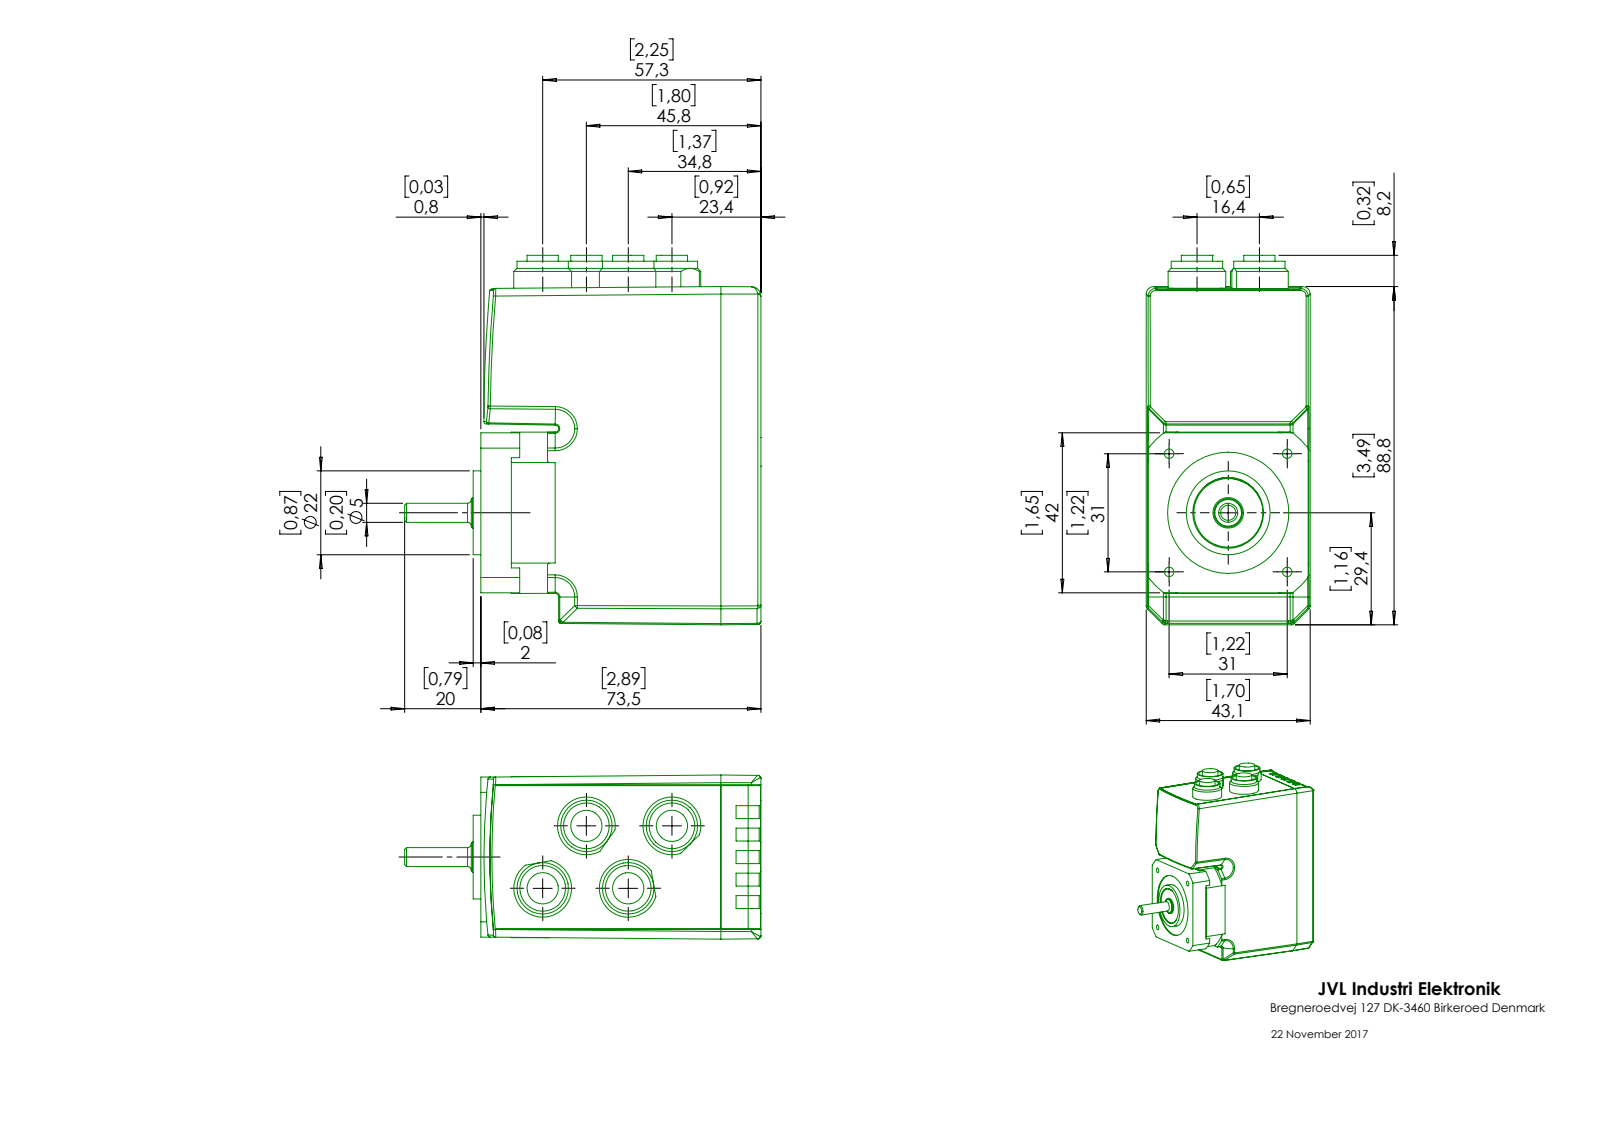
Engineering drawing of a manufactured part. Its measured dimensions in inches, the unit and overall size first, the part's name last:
Units: inches
Overall size (bounding box): 3.817 × 3.681 × 1.695
Round holes (diameter × count): ⌀0.059 ×6, ⌀0.098 ×4, ⌀0.472 ×4, ⌀0.13 ×1, ⌀0.327 ×1, ⌀1.252 ×1
Round bosses / shafts (diameter × count): ⌀0.596 ×4, ⌀0.531 ×4, ⌀0.323 ×4, ⌀0.866 ×1, ⌀0.315 ×1, ⌀0.295 ×1, ⌀0.197 ×1
Partial cylindrical surfaces — rounded edges, fillets, slot ends (radius × count): R0.039 ×30, R0.031 ×3, R0.037 ×2, R0.079 ×2, R0.15 ×2, R0.165 ×2, R0.014 ×1, R0.024 ×1
Main face-to-face distances: 1.696, 1.659, 2.89, 1.665, 2.894, 1.654, 0.02, 2.87, 2.874, 0.014
Hole centre spacings: 0.198, 0.754, 0.863, 1.024, 1.22, 1.256, 1.608, 0.787
Volume: 16.18 in³ · Surface area: 49.02 in²
Bodies: 1 solid, 452 faces (182 planar, 152 cylindrical, 118 other)
Part name (STEP PRODUCT): MIS171 M12 TOP Ø5
STEP written by: SolidWorks 2017 (CONFIG_CONTROL_DESIGN)
